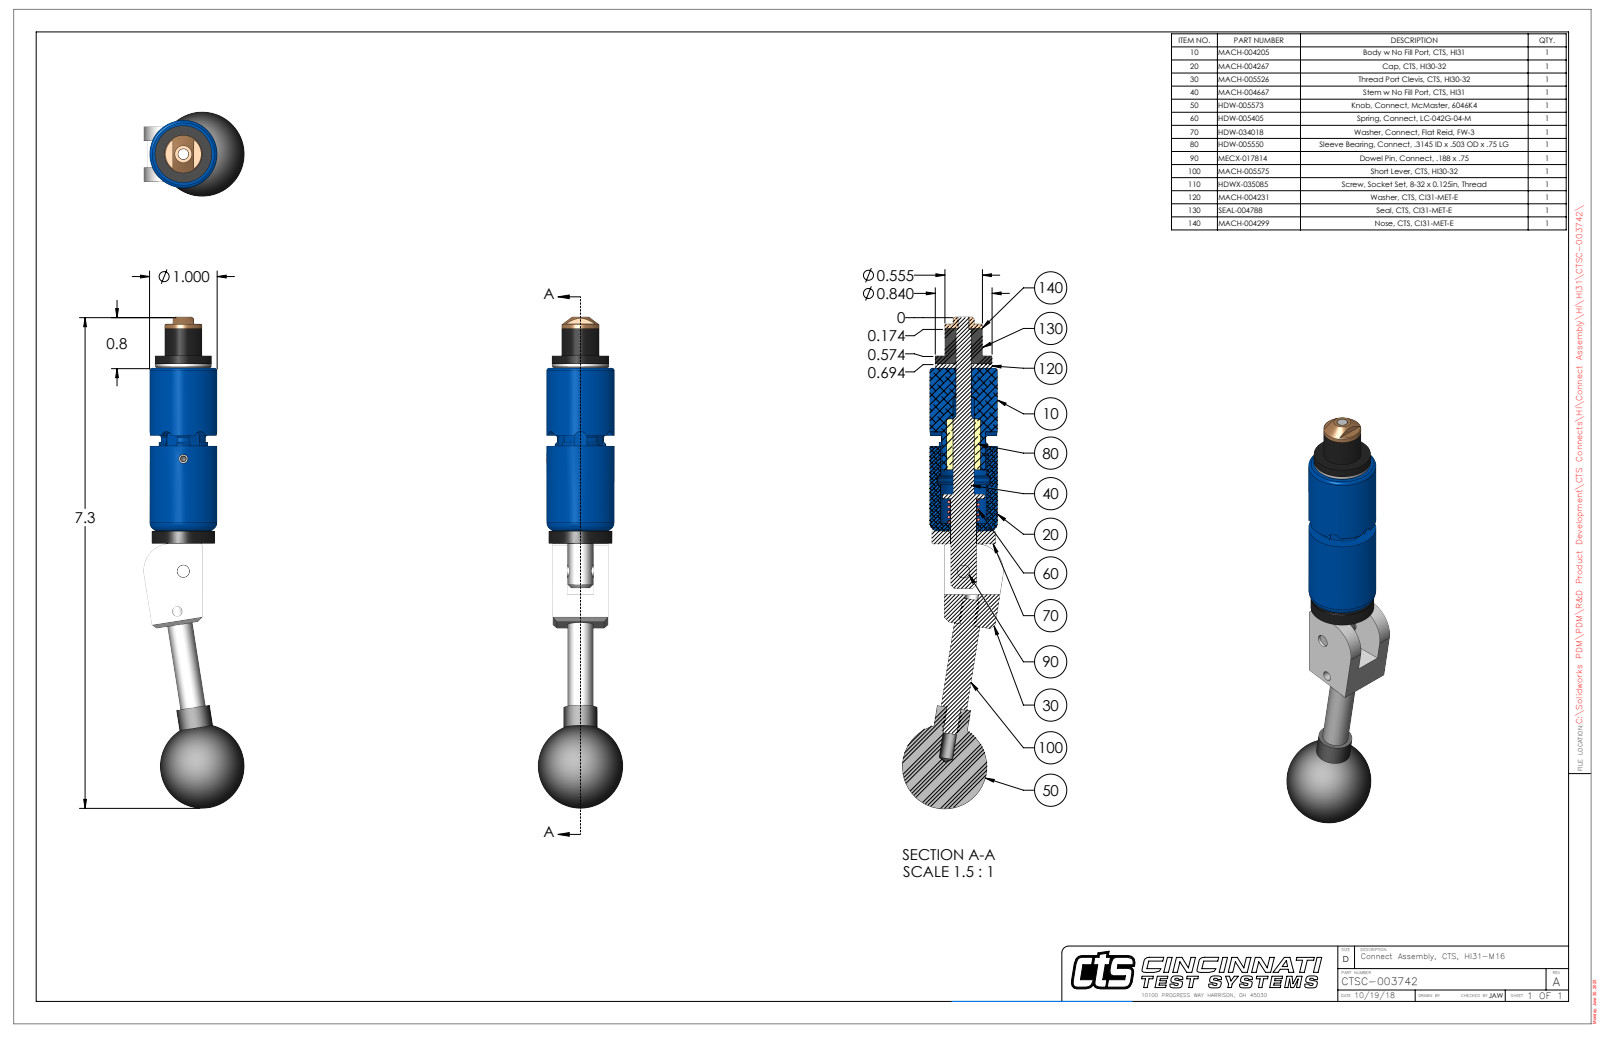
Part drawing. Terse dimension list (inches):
name: CTSC-003742
written by: SolidWorks 2023 (AUTOMOTIVE_DESIGN)
unit: in
bodies: 9 solids, 268 faces (101 planar, 109 cylindrical, 58 other)
size: 7.256 × 1.492 × 1.25
volume: 3.967 in³; area: 32.95 in²
holes: 2× ⌀0.201, 1× ⌀0.136, 1× ⌀0.15, 1× ⌀0.159, 1× ⌀0.189, 1× ⌀0.218, 1× ⌀0.228, 1× ⌀0.229, 1× ⌀0.385, 1× ⌀0.392, 1× ⌀0.688
bosses: 1× ⌀1, 1× ⌀0.936, 1× ⌀0.84, 1× ⌀0.837, 1× ⌀0.555, 1× ⌀0.555, 1× ⌀0.5, 1× ⌀0.38
rounds: 6× R0.093, 2× R0.029, 1× R0.375, 1× R0.4, 1× R0.467
face distances: 0.21, 0.602, 0.06, 2.465, 2.405, 0.812, 2.652, 2.592, 0.187, 0.391
hole spacings: 0.599, 1.658, 2.252
